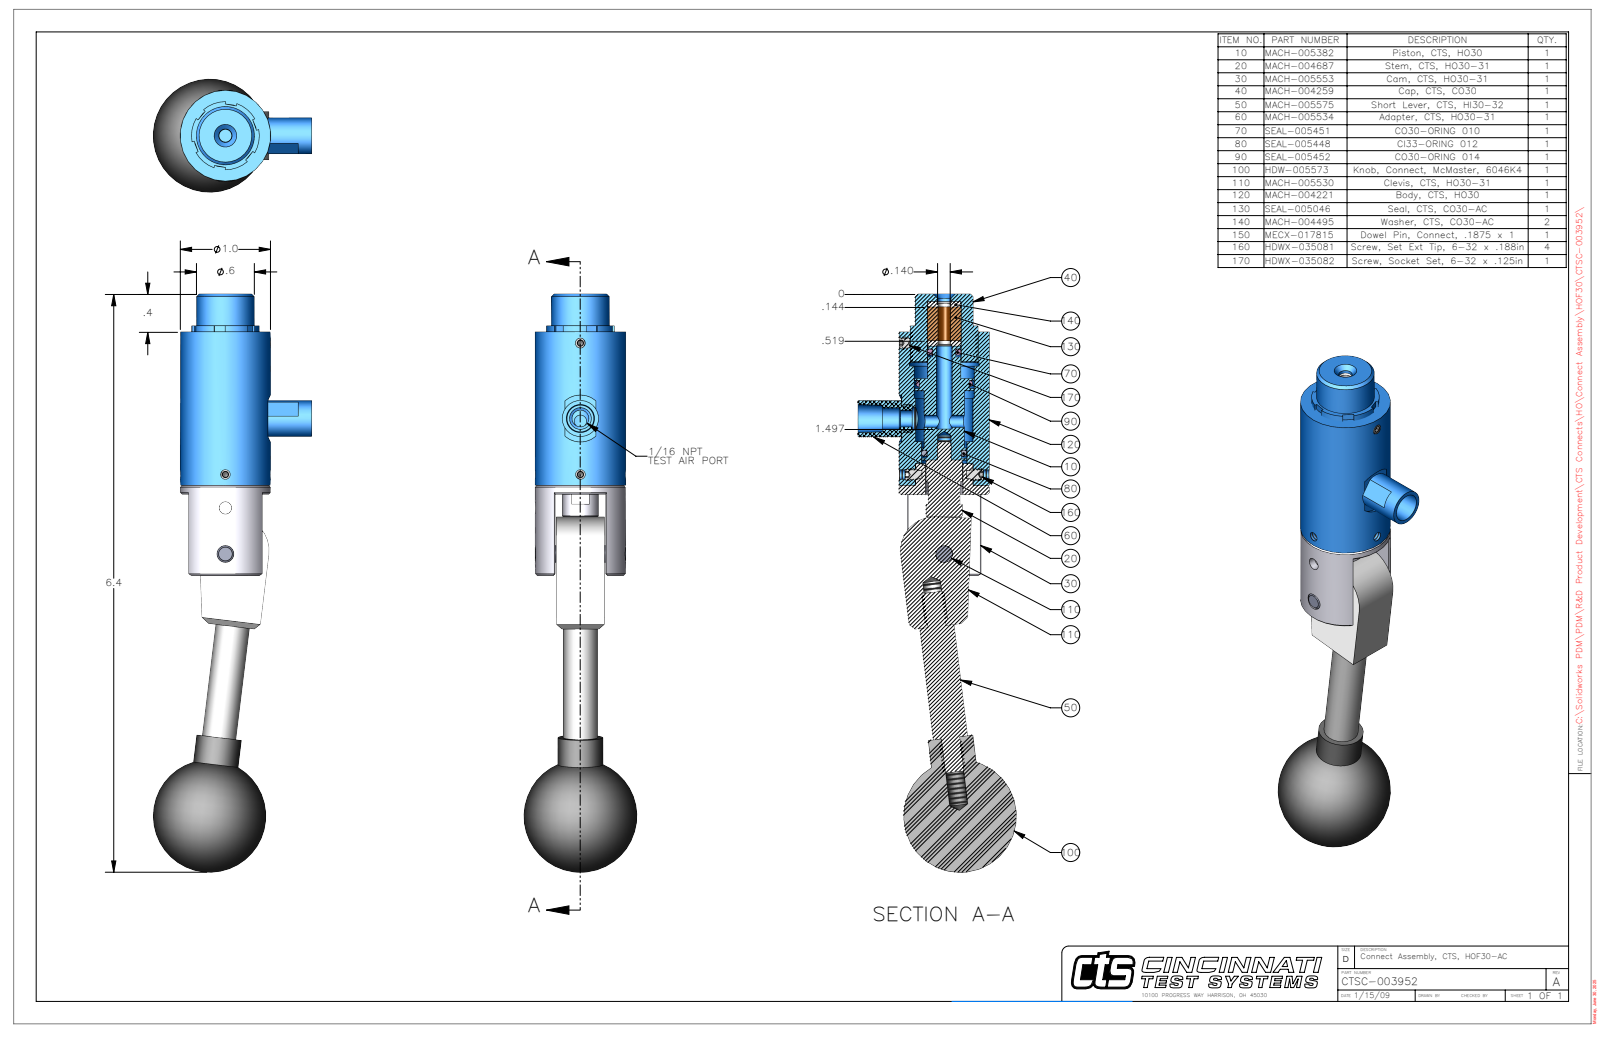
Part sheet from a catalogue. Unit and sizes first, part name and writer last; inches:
Units: inches
Overall size (bounding box): 6.407 × 1.755 × 1.25
Round holes (diameter × count): ⌀0.107 ×3, ⌀0.201 ×2, ⌀0.136 ×1, ⌀0.138 ×1, ⌀0.14 ×1, ⌀0.142 ×1, ⌀0.15 ×1, ⌀0.15 ×1, ⌀0.175 ×1, ⌀0.187 ×1, ⌀0.189 ×1, ⌀0.19 ×1
Round bosses / shafts (diameter × count): ⌀0.138 ×3, ⌀0.4 ×2, ⌀0.092 ×2, ⌀1 ×1, ⌀0.642 ×1, ⌀0.63 ×1, ⌀0.5 ×1, ⌀0.49 ×1
Partial cylindrical surfaces — rounded edges, fillets, slot ends (radius × count): R0.26 ×1, R0.349 ×1, R0.374 ×1, R0.375 ×1
Main face-to-face distances: 0.012, 0.542, 0.53, 0.554, 1.8, 0.059, 0.434, 1.241, 2.22, 0.42
Hole centre spacings: 0.03, 0.37, 0.51, 0.59, 0.62, 0.835, 0.865, 0.88
Volume: 3.39 in³ · Surface area: 32.88 in²
Bodies: 13 solids, 460 faces (168 planar, 161 cylindrical, 131 other)
Part name (STEP PRODUCT): CTSC-003952
STEP written by: SolidWorks 2023 (AUTOMOTIVE_DESIGN)
